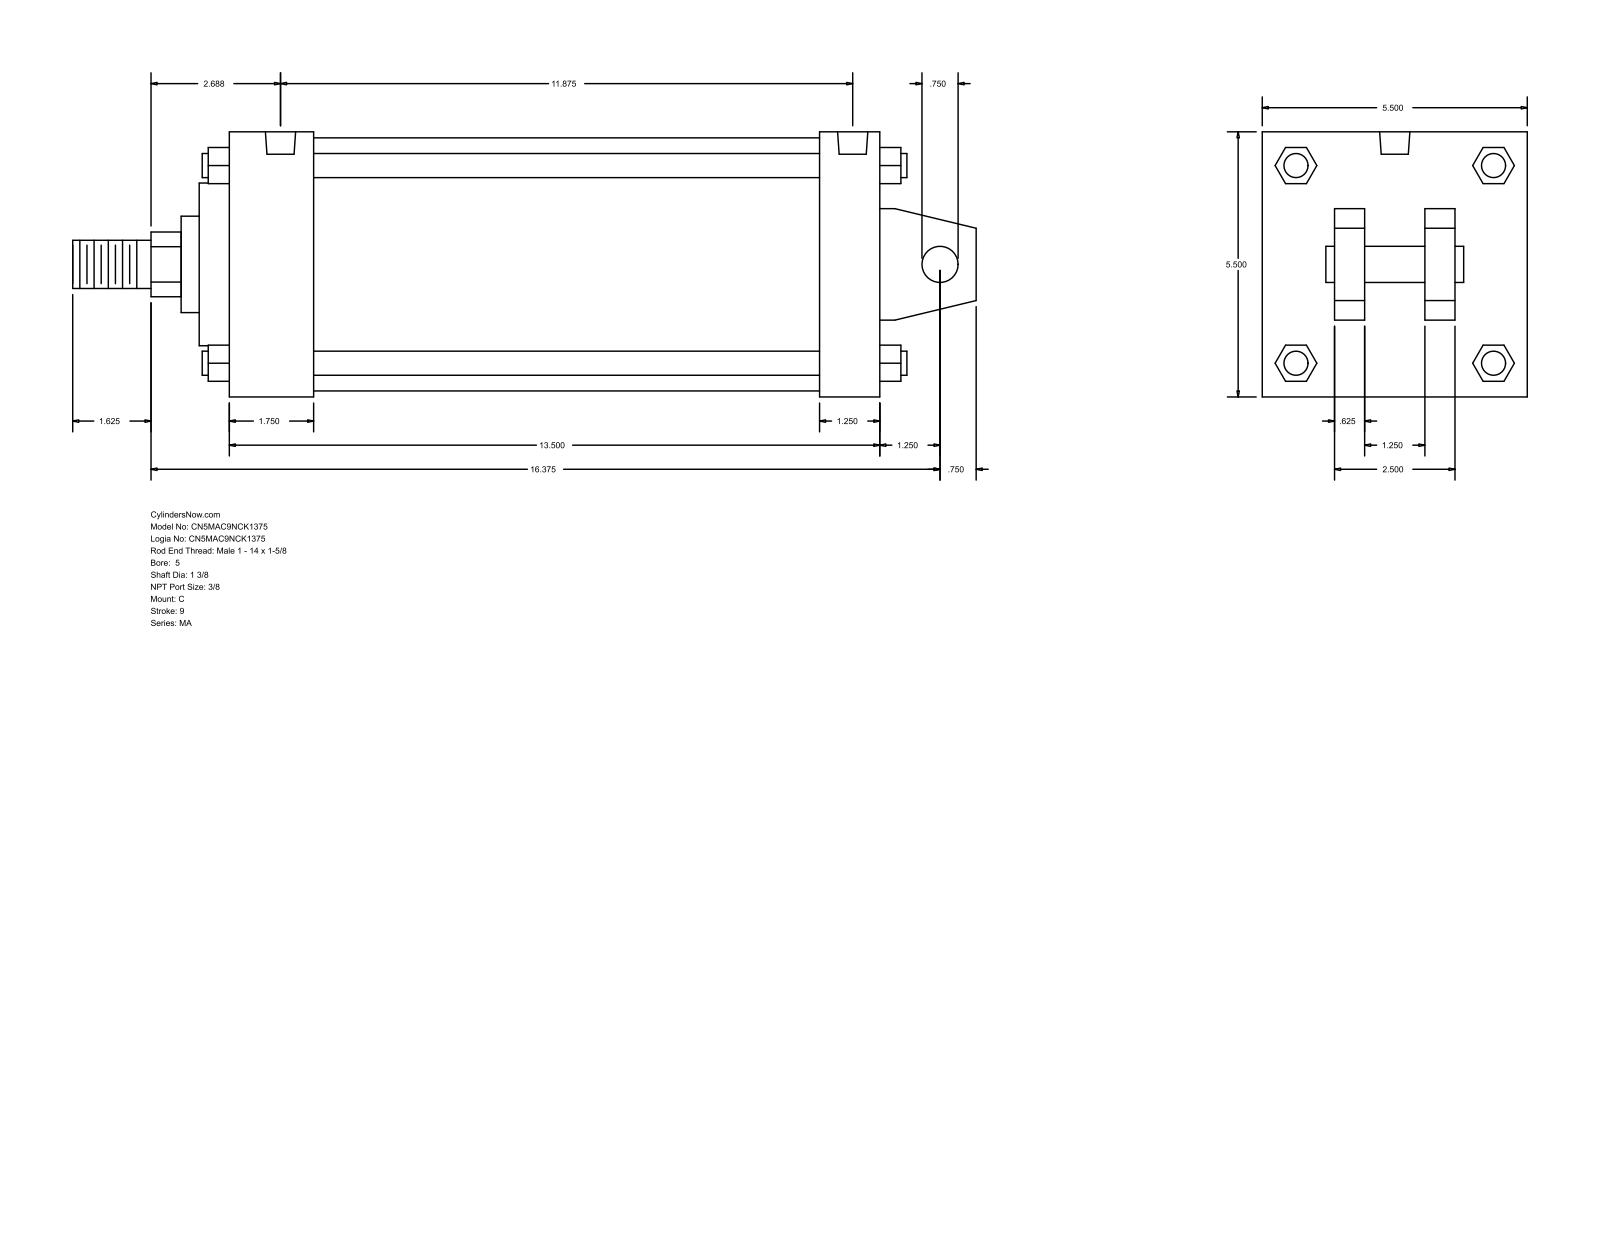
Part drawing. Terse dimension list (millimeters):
name: MA_C__0500_1.375
written by: GSSL Pune (CONFIG_CONTROL_DESIGN)
unit: mm
bodies: 0 solids, 141 faces (109 planar, 32 cylindrical, 0 other)
size: 476.25 × 139.7 × 139.7
holes: 4× ⌀11.11, 2× ⌀15.93
bosses: 4× ⌀12.7, 1× ⌀133.35, 1× ⌀85.72, 1× ⌀50.8, 1× ⌀34.92, 1× ⌀25.4, 1× ⌀19.05
rounds: 1× R17.06
face distances: 139.7, 342.91, 15.87, 311.16, 31.75, 44.45, 266.71, 298.46, 53.97, 38.1
hole spacings: 4.77, 292.09, 296.86, 301.63
